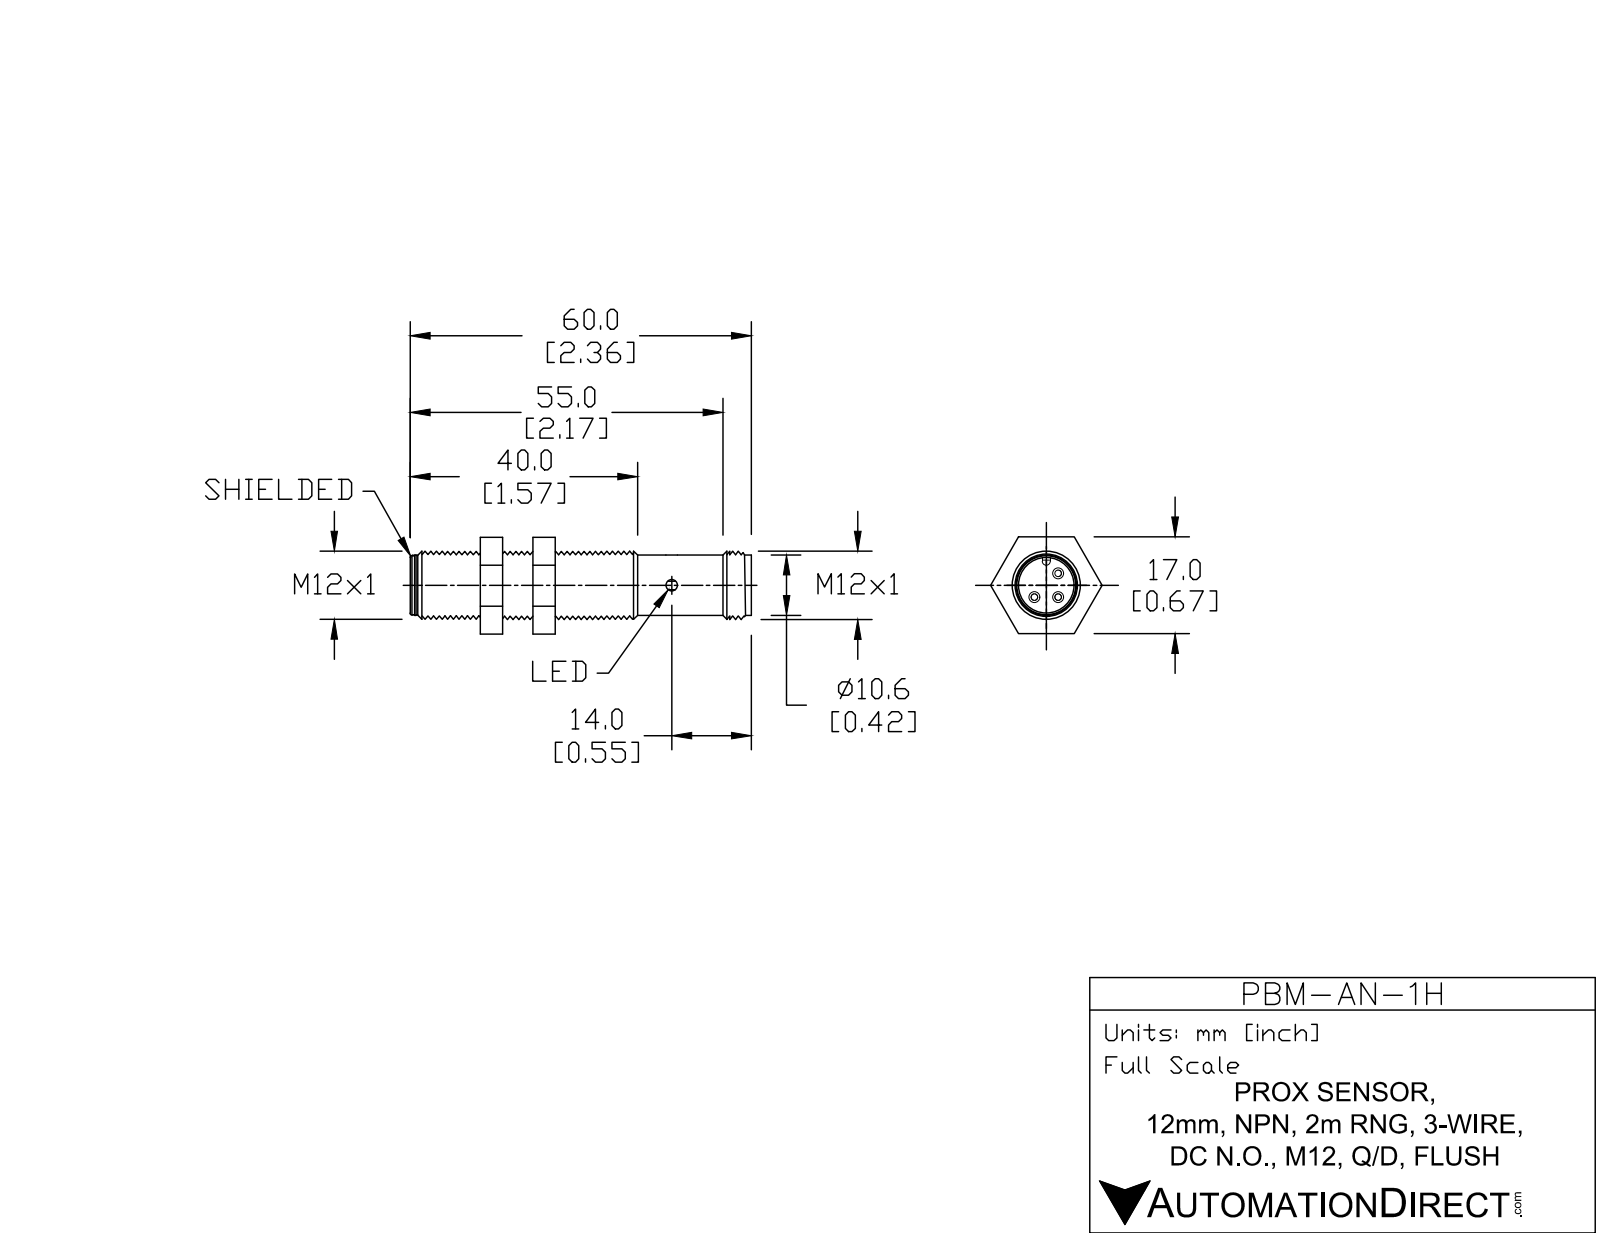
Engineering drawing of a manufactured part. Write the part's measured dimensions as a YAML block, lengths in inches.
part_name: "PBM-AN-1H"
step_written_by: "SolidWorks 2011 (AUTOMOTIVE_DESIGN)"
units: inches
bodies: {solids: 9, faces: 66, planar: 38, cylindrical: 17, other: 11}
overall_size: [2.343, 0.773, 0.674]
volume: 0.427
surface_area: 7.731
round_holes:
  - {diameter: 0.059, count: 1}
  - {diameter: 0.138, count: 1}
  - {diameter: 0.331, count: 1}
  - {diameter: 0.404, count: 1}
  - {diameter: 0.472, count: 1}
round_bosses_or_shafts:
  - {diameter: 0.039, count: 3}
  - {diameter: 0.423, count: 1}
  - {diameter: 0.418, count: 1}
  - {diameter: 0.413, count: 1}
partial_cylinders:
  - {radius: 0.02, count: 1}
face_to_face_distances: [0.669, 0.394, 0.157, 1.25, 1.093, 0.236, 1.063, 0.551, 1.22, 0.827]
